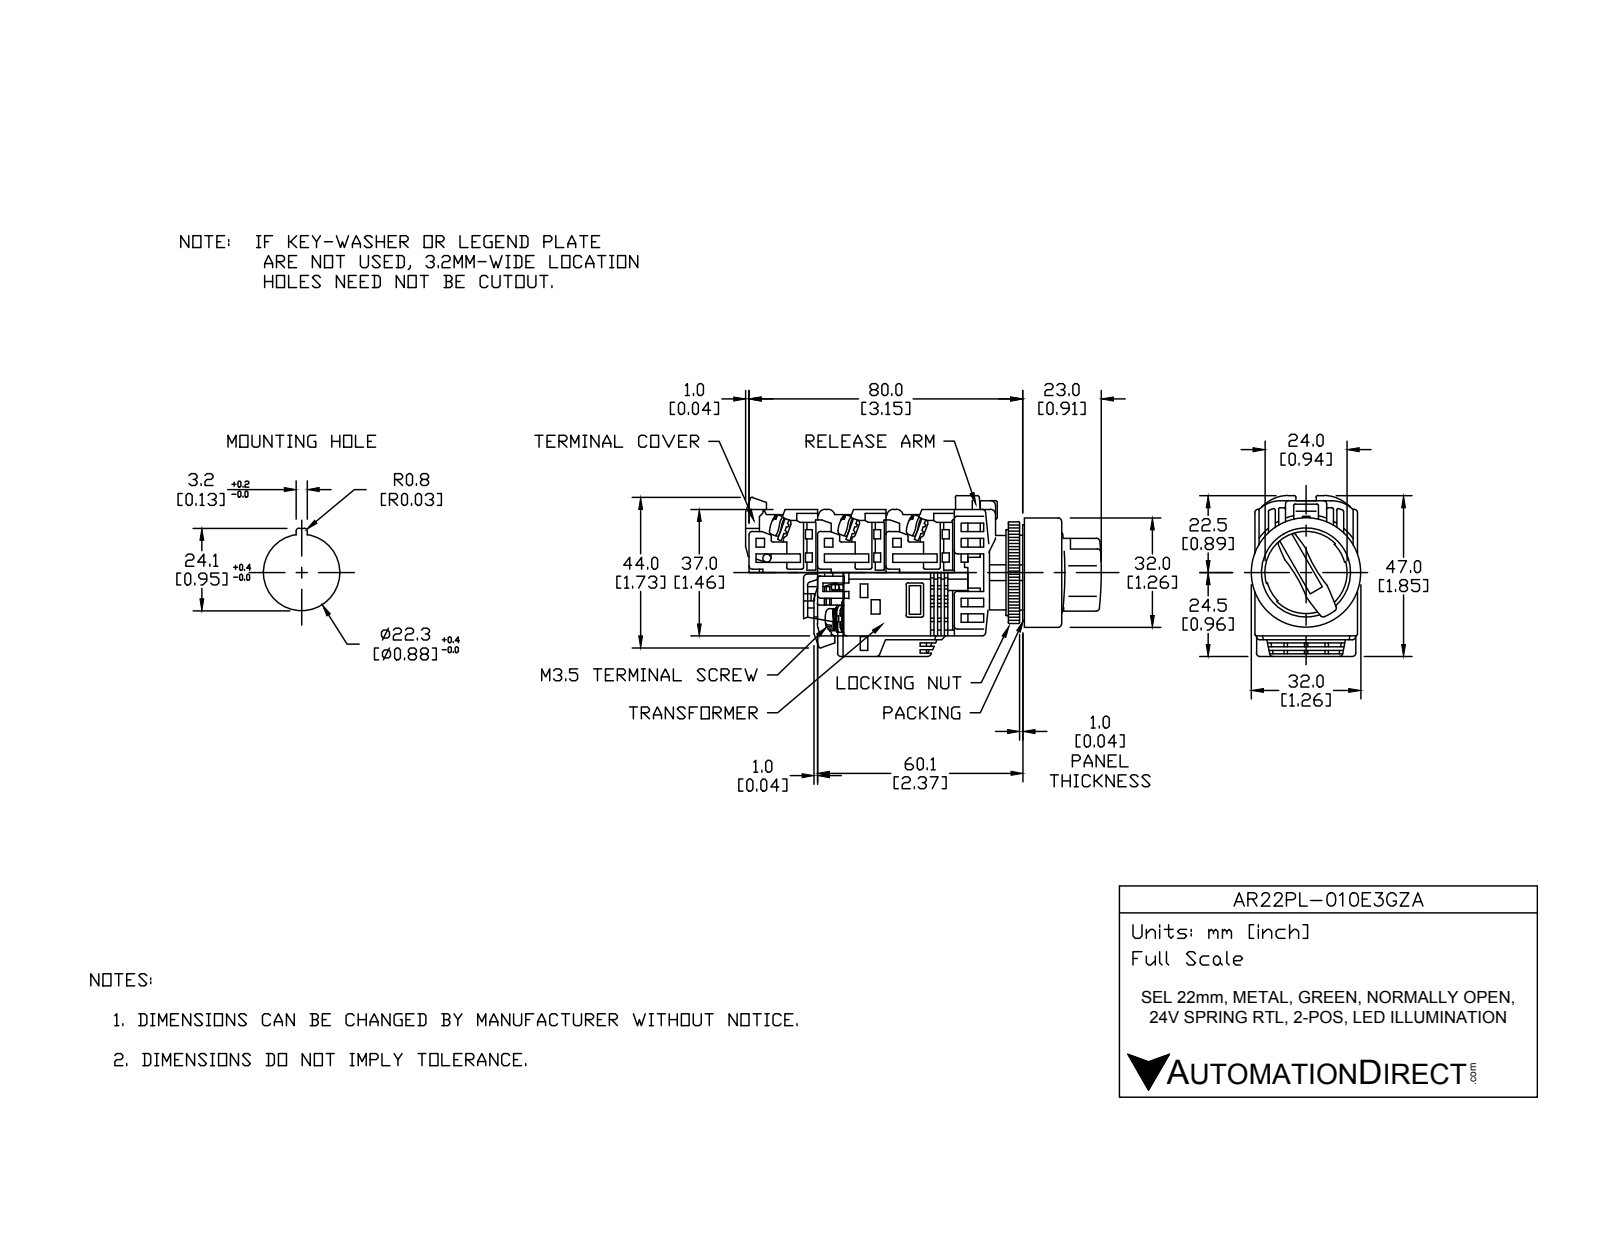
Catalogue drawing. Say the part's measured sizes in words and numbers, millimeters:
The part is named "AR22PL-010E3GZA". Its 3-D file was written by "SolidWorks 2017 (AUTOMOTIVE_DESIGN)". It is 18 solids with 462 faces: 317 planar, 118 cylindrical and 27 other. Overall it measures 64.5 by 43.81 by 32 millimeters. Its volume is 38 531 cubic millimeters and its surface area 24 831 square millimeters. Round holes: 1 of diameter 21.8, 1 of diameter 22, 1 of diameter 25, 1 of diameter 31. Round bosses or shafts: 4 of diameter 5, 1 of diameter 32, 1 of diameter 30.5, 1 of diameter 29.8, 1 of diameter 24, 1 of diameter 21.75, 1 of diameter 17. Partial cylindrical surfaces (rounded edges, fillets, slot ends): 39 of radius 0.5, 8 of radius 1.75, 6 of radius 1, 4 of radius 5, 2 of radius 4, 1 of radius 12, 1 of radius 16.59, 1 of radius 17.59. The main face-to-face distances are 1, 18, 3, 28.5, 48.5, 20, 29, 0.5, 2, 31.
